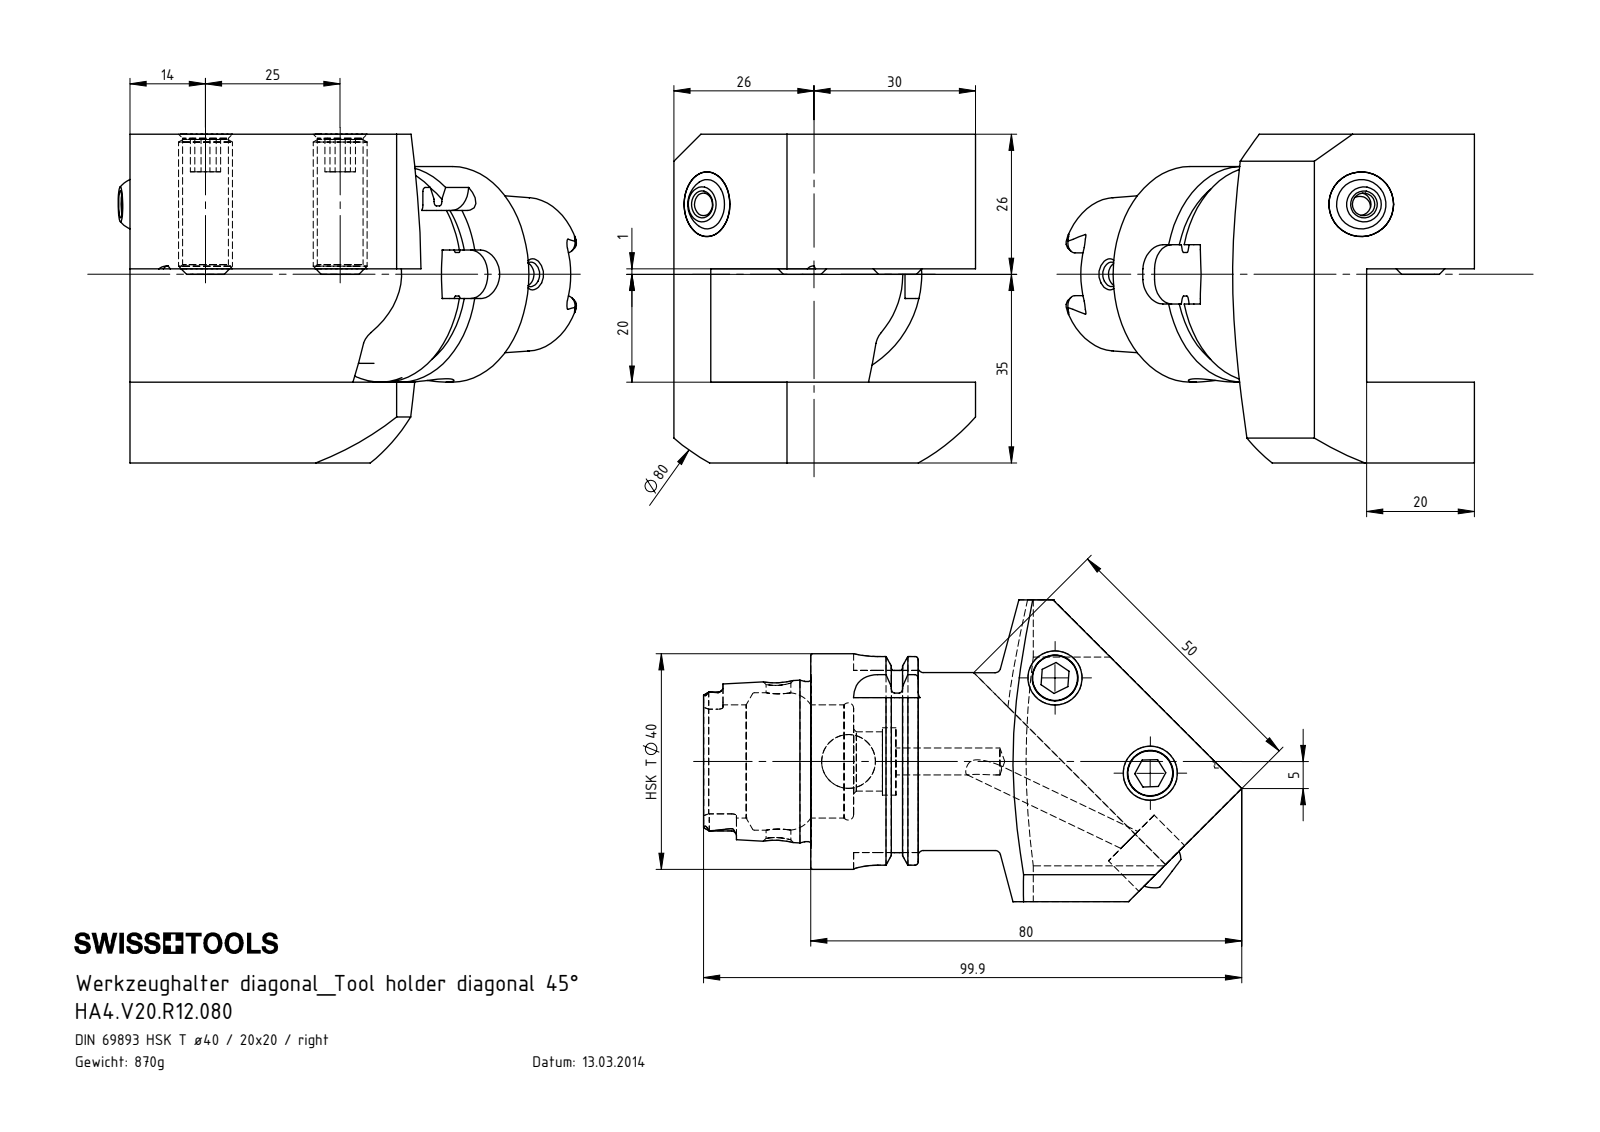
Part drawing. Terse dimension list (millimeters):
name: KU1-U12.001.010; KU1-U12.001.010_2; ISO 4026 - M10 x 25; HA4.V20.R12.080 (+2 more)
written by: SolidWorks 2017 (AUTOMOTIVE_DESIGN)
unit: mm
bodies: 5 solids, 239 faces (79 planar, 67 cylindrical, 93 other)
size: 99.9 × 61 × 56
volume: 111 148 mm³; area: 27 799 mm²
holes: 2× ⌀4.2, 2× ⌀8.5, 1× ⌀4.6, 1× ⌀5, 1× ⌀7, 1× ⌀10, 1× ⌀11, 1× ⌀12, 1× ⌀12.5, 1× ⌀21, 1× ⌀25.5
bosses: 2× ⌀10, 1× ⌀40, 1× ⌀34.75, 1× ⌀33, 1× ⌀29.71
rounds: 6× R0.9, 4× R1.88, 4× R4.5, 1× R40
face distances: 61, 20, 15, 46, 25, 36, 21, 7.95, 8, 19.95
hole spacings: 25, 41.37, 56.07
